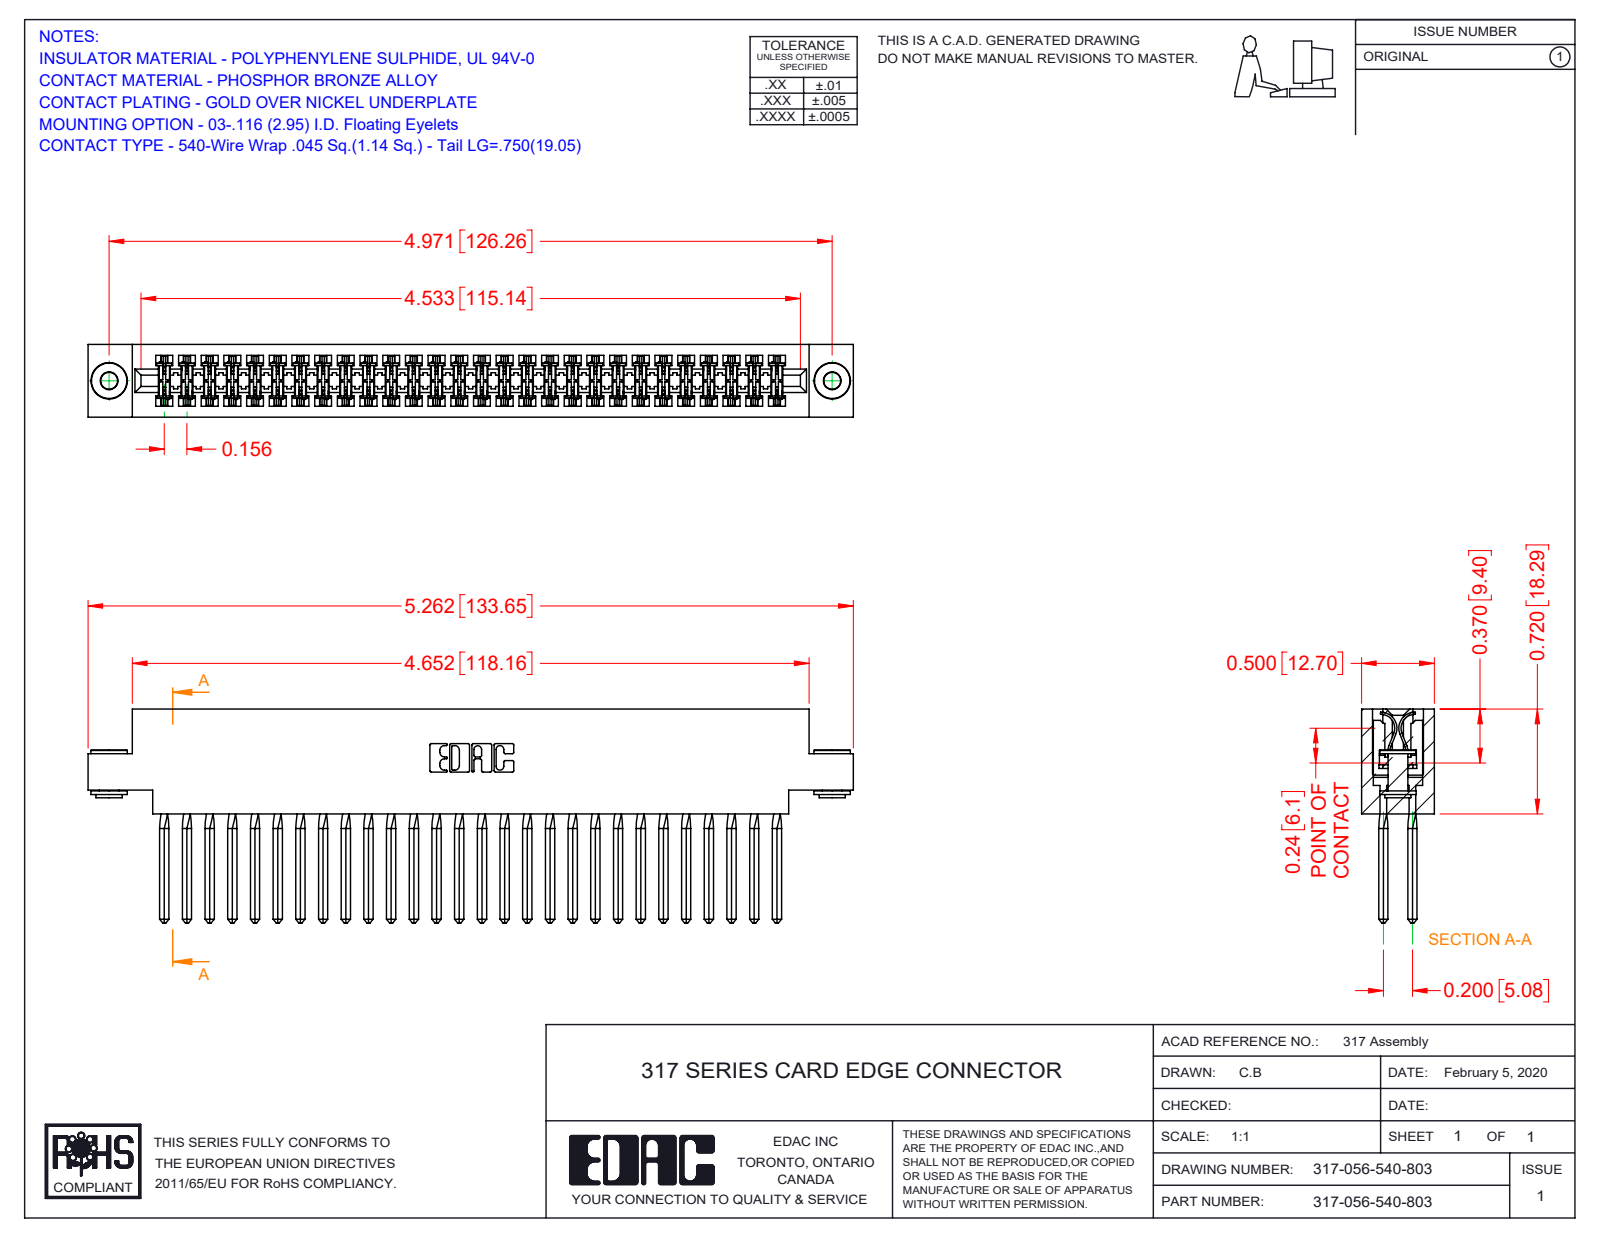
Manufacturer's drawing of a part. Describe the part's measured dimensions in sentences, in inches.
The part is named "317-056-540-803; 317-290-001_540; 345-250-002_345-250-002-102; 317 Part_.156 Dia - TH". Its 3-D file was written by "SolidWorks 2016 (CONFIG_CONTROL_DESIGN)". It is 59 solids with 5124 faces: 4156 planar, 736 cylindrical and 232 other. Overall it measures 5.262 by 1.47 by 0.5 inches. Its volume is 1.341 cubic inches and its surface area 50.3 square inches. Round holes: 2 of diameter 0.116, 2 of diameter 0.156. Round bosses or shafts: 2 of diameter 0.25, 2 of diameter 0.18, 2 of diameter 0.136. Partial cylindrical surfaces (rounded edges, fillets, slot ends): 112 of radius 0.015, 22 of radius 0.01, 6 of radius 0.007, 6 of radius 0.031, 3 of radius 0.026, 2 of radius 0.095, 2 of radius 0.1, 2 of radius 0.11. The main face-to-face distances are 0.5, 0.075, 0.425, 0.35, 0.11, 0.195, 0.094, 0.2, 0.72, 0.115. The hole center spacings are 4.971.
